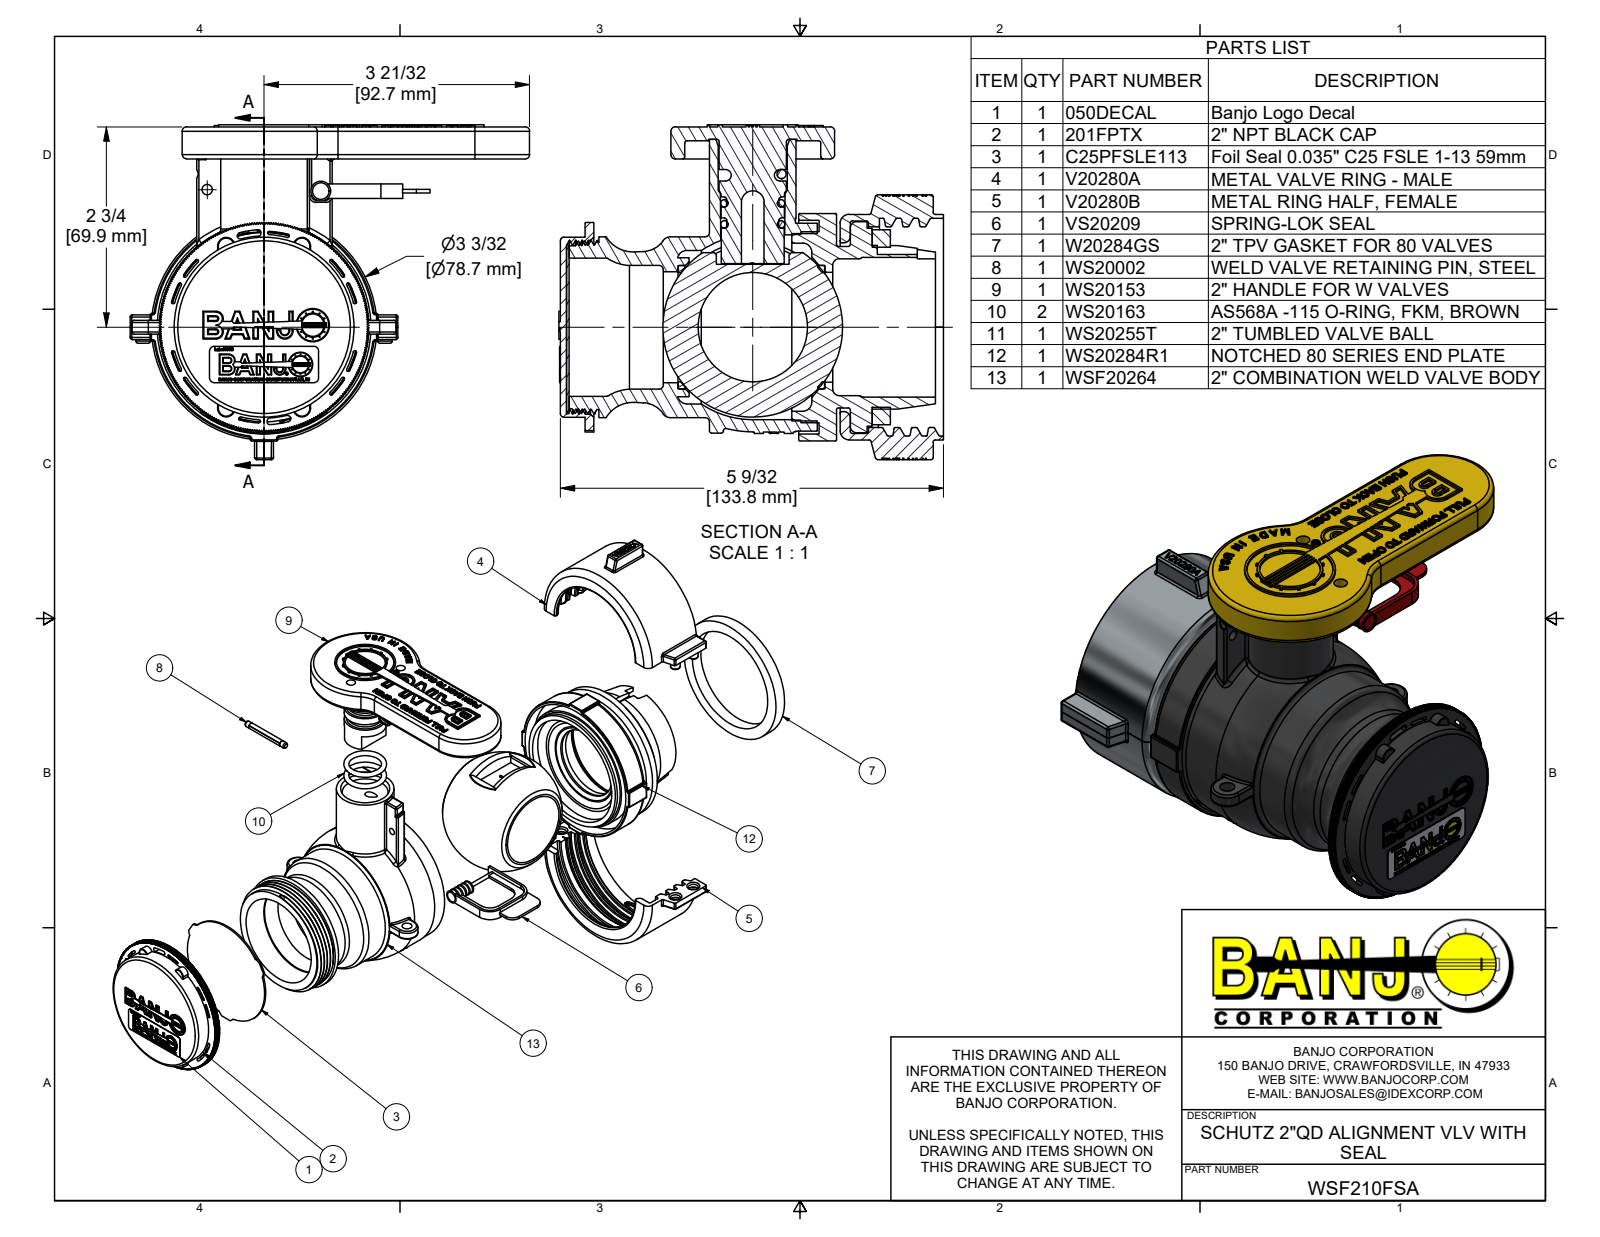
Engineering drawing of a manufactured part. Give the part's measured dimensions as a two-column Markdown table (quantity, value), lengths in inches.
| quantity | value |
| --- | --- |
| part name | WSF210FSA; 201FPTX; 050DECAL; C25PFSLE113 (+8 more) |
| STEP written by | Autodesk Inventor 2022 (AUTOMOTIVE_DESIGN) |
| units | inches |
| bodies | 16 solids, 4672 faces (2451 planar, 991 cylindrical, 1230 other) |
| overall size | 5.49 × 5.287 × 4.603 |
| volume | 20.2 in³ |
| surface area | 265.8 in² |
| round holes (diameter × count) | 0.208 × 4, 0.257 × 4, 0.145 × 2, 0.188 × 2, 0.207 × 2, 1.5 × 2, 0.089 × 1, 0.156 × 1, 0.227 × 1, 0.309 × 1, 0.312 × 1, 0.321 × 1 |
| round bosses / shafts (diameter × count) | 0.2 × 4, 2.25 × 2, 3.1 × 1, 3.05 × 1, 2.92 × 1, 2.9 × 1, 2.88 × 1, 2.858 × 1 |
| partial cylindrical surfaces (radius × count) | 0.03 × 78, 0.016 × 32, 0.06 × 4, 0.062 × 4, 0.118 × 4, 0.25 × 4, 0.069 × 3, 0.225 × 3 |
| main face-to-face distances | 0.19, 0.12, 0.085, 0.035, 0.035, 0.085, 4.167, 4.202, 4.202, 4.287 |
| hole center spacings | 0.524, 1.562, 1.633, 2.045, 2.256, 2.361, 2.513, 2.78 |
